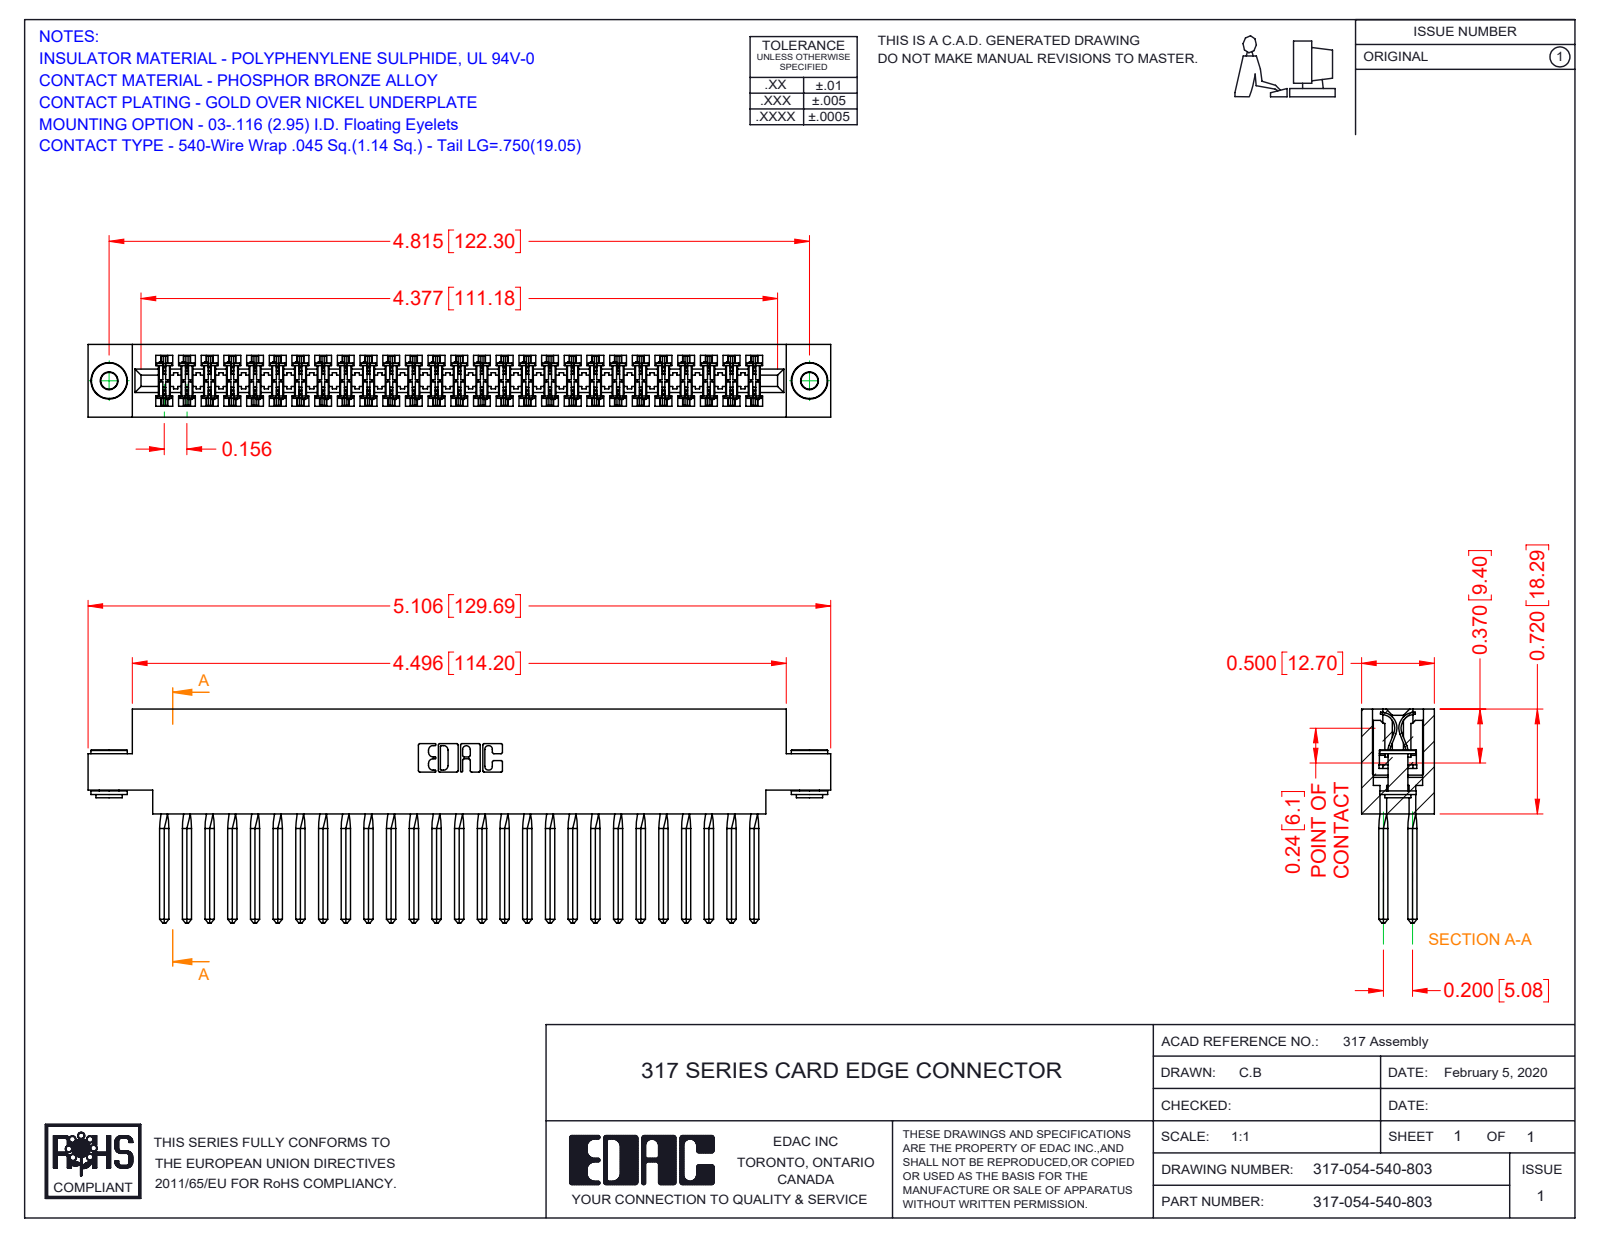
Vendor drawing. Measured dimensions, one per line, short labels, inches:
name: 345-250-002_345-250-002-102; 317 Part_.156 Dia - TH; 317-054-540-803; 317-290-001_540
written by: SolidWorks 2016 (CONFIG_CONTROL_DESIGN)
unit: in
bodies: 57 solids, 4946 faces (4010 planar, 712 cylindrical, 224 other)
size: 5.106 × 1.47 × 0.5
volume: 1.299 in³; area: 48.63 in²
holes: 2× ⌀0.116, 2× ⌀0.156
bosses: 2× ⌀0.25, 2× ⌀0.18, 2× ⌀0.136
rounds: 108× R0.015, 22× R0.01, 6× R0.007, 6× R0.031, 3× R0.026, 2× R0.095, 2× R0.1, 2× R0.11
face distances: 0.5, 0.075, 0.425, 0.35, 0.11, 0.195, 0.094, 0.72, 0.2, 0.115
hole spacings: 4.815
